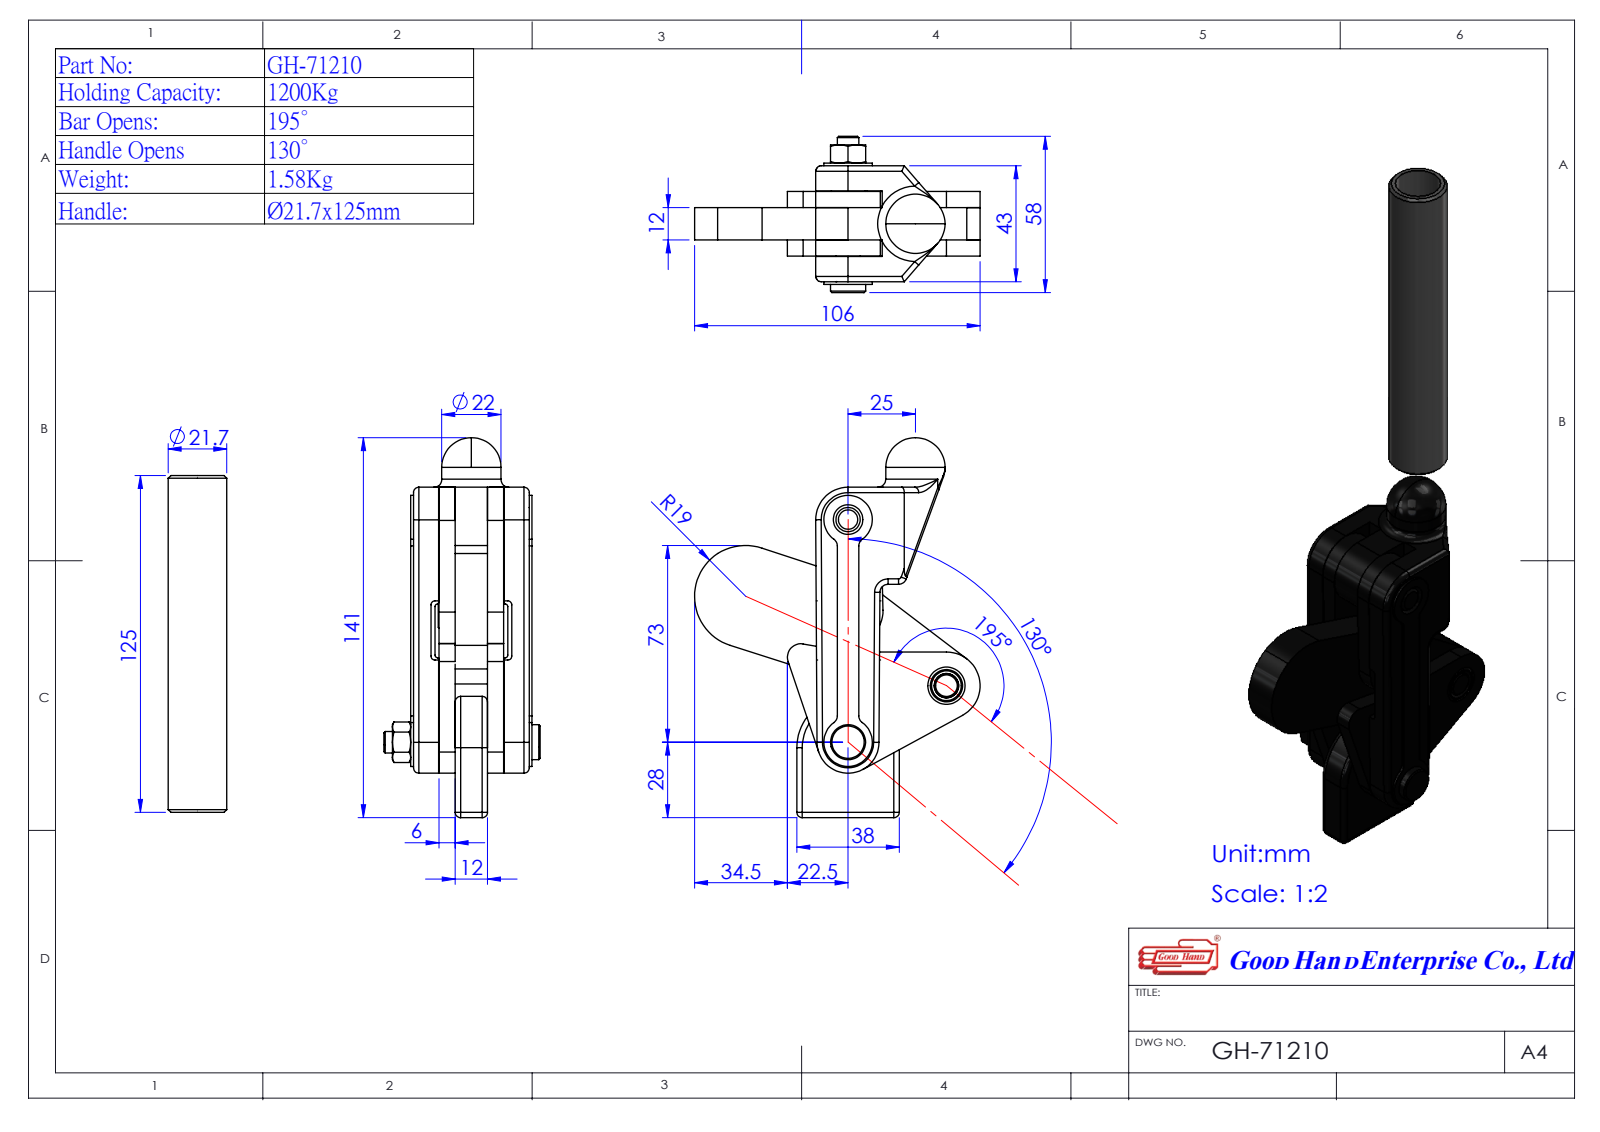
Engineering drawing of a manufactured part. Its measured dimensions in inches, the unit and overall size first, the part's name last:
Units: inches
Overall size (bounding box): 10.496 × 4.174 × 2.283
Round holes (diameter × count): ⌀0.315 ×4, ⌀0.634 ×1
Round bosses / shafts (diameter × count): ⌀0.709 ×2, ⌀0.866 ×1, ⌀0.854 ×1, ⌀0.512 ×1
Partial cylindrical surfaces — rounded edges, fillets, slot ends (radius × count): R0.079 ×14, R0.118 ×6, R0.472 ×2, R0.197 ×1, R0.433 ×1, R0.453 ×1, R0.492 ×1, R0.748 ×1
Main face-to-face distances: 0.472, 0.236, 0.709, 0.242, 0.715, 0.951, 0.945, 0.368, 0.374, 0.61
Hole centre spacings: 1.339, 1.658, 1.773, 1.914, 2.821, 3.252
Volume: 12.62 in³ · Surface area: 110.6 in²
Bodies: 6 solids, 201 faces (72 planar, 96 cylindrical, 33 other)
Part name (STEP PRODUCT): Group4^GH-71210(簡化); GH-71210(簡化); 4702108-1-1^GH-71210(簡化); 471210125 (+3 more)
STEP written by: SolidWorks 2016 (AUTOMOTIVE_DESIGN)
